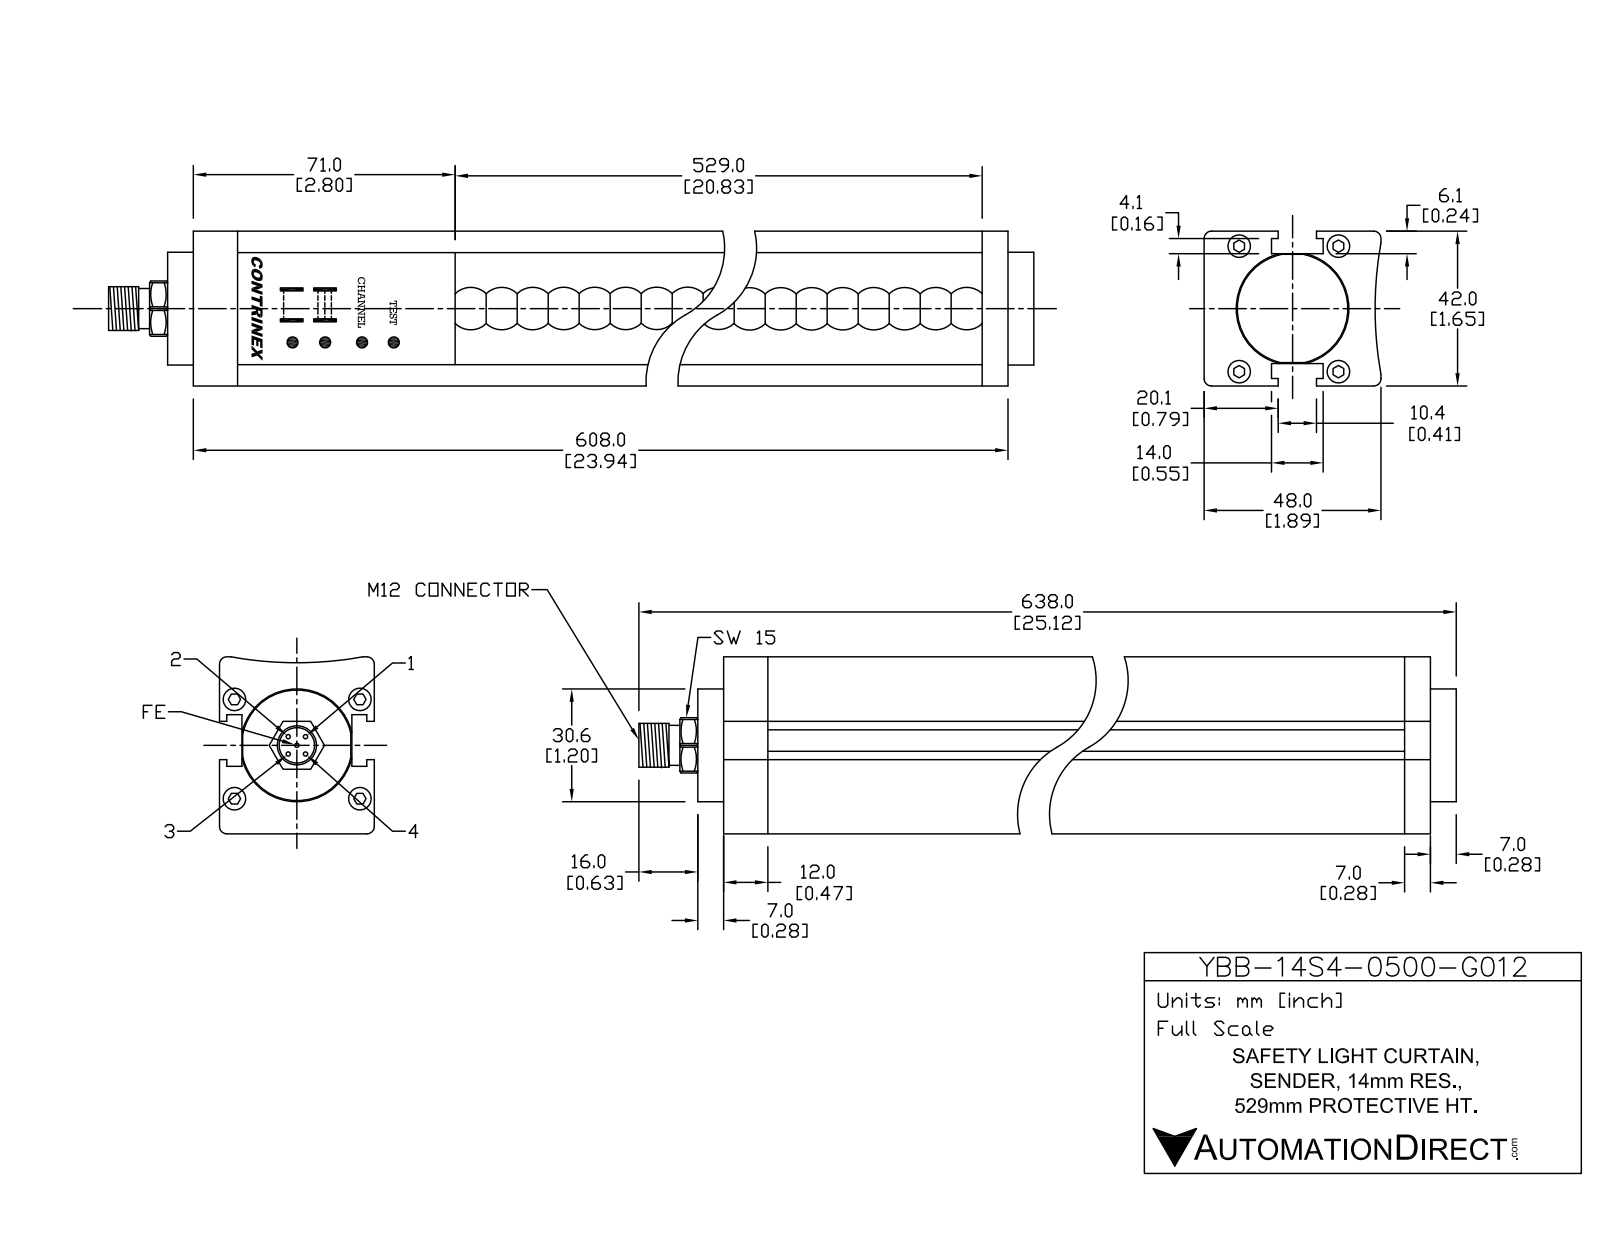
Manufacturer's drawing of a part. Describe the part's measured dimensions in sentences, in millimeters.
The part is named "YBB-14S4-0500-G012". Its 3-D file was written by "SolidWorks 2016 (AUTOMOTIVE_DESIGN)". It is 19 solids with 440 faces: 208 planar, 168 cylindrical and 64 other. Overall it measures 638 by 48 by 42 millimeters. Its volume is 1 099 000 cubic millimeters and its surface area 147 436 square millimeters. Round holes: 4 of diameter 6, 1 of diameter 8.5, 1 of diameter 32. Round bosses or shafts: 5 of diameter 1, 4 of diameter 5.5, 1 of diameter 30.6, 1 of diameter 12, 1 of diameter 10.5. Partial cylindrical surfaces (rounded edges, fillets, slot ends): 48 of radius 1, 4 of radius 0.5, 2 of radius 0.55, 1 of radius 8.2, 1 of radius 100. The main face-to-face distances are 6.3, 35.7, 42, 29.4, 14, 17.2, 31.2, 588, 15.7, 29.7. The hole center spacings are 21.04, 22.34, 26.9, 34, 43.35.
